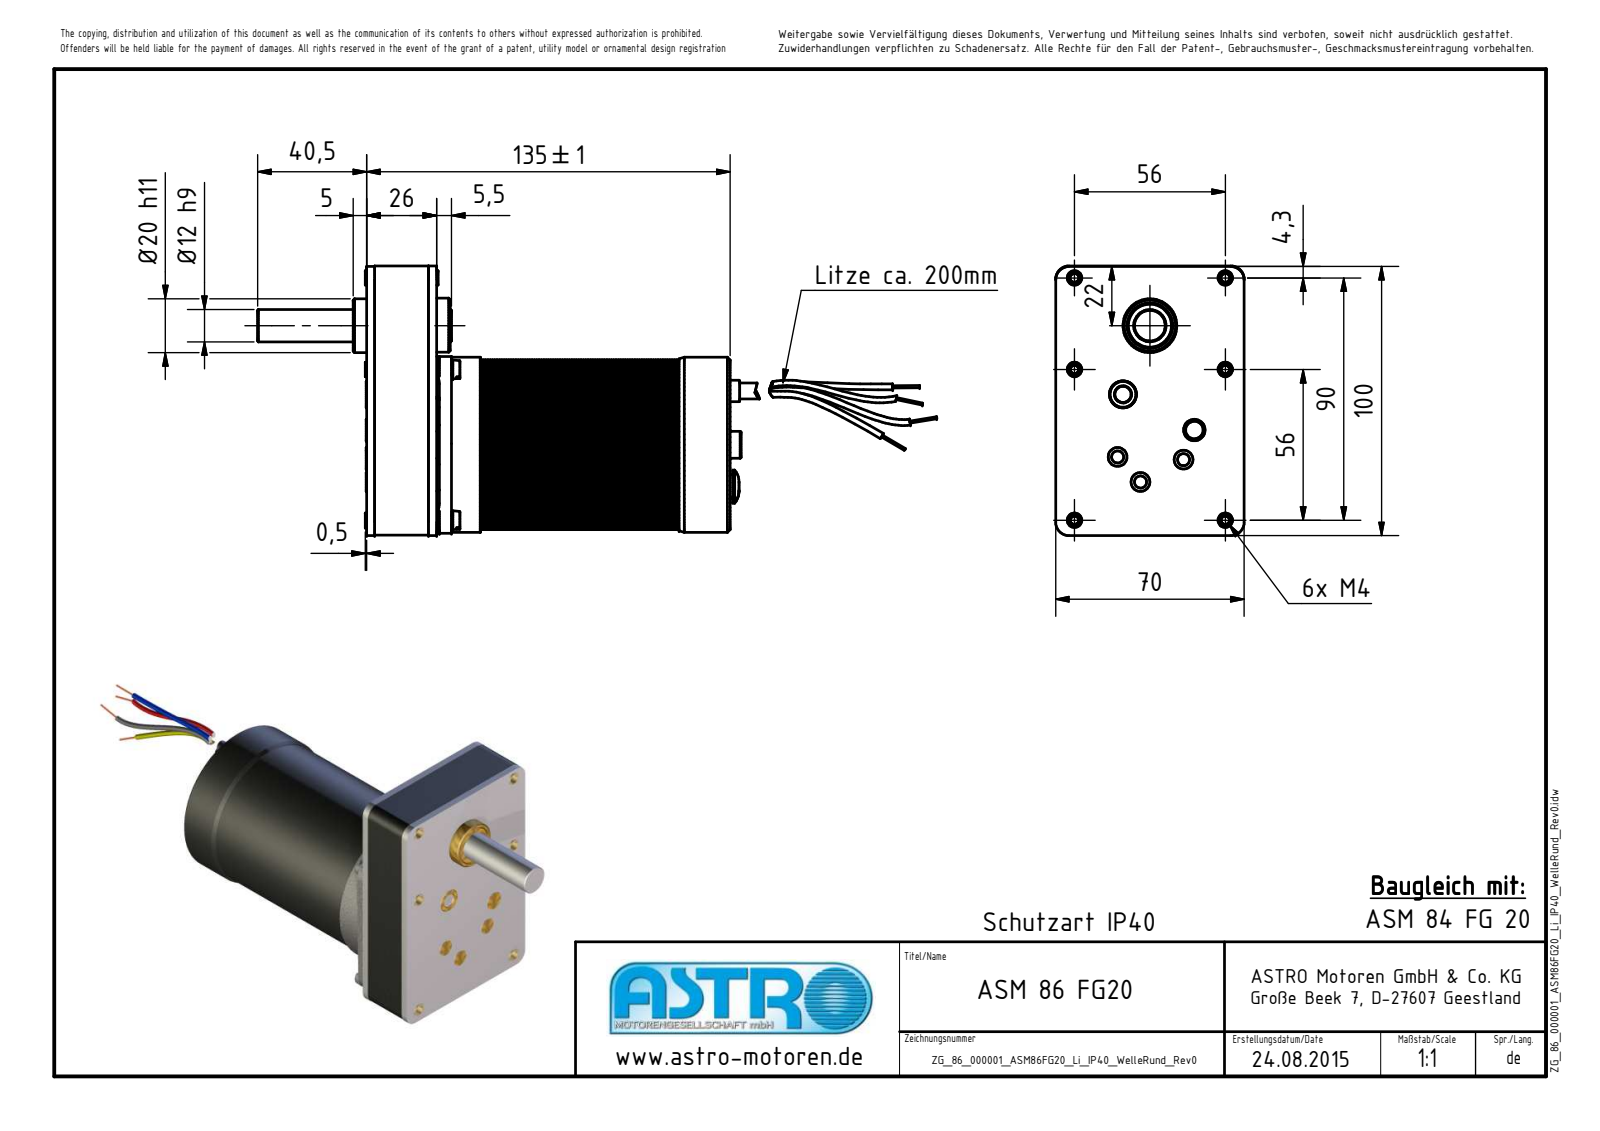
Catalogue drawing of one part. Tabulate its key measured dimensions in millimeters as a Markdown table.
| quantity | value |
| --- | --- |
| part name | ZG_86_000001_ASM86FG20_Li_IP40_WelleRund_Rev0; AFG-20rund; FG-Antriebsseite20; FG-Abstandhalter (+8 more) |
| STEP written by | Autodesk Inventor 2010 (AUTOMOTIVE_DESIGN) |
| units | millimeters |
| bodies | 148 solids, 17698 faces (6422 planar, 11163 cylindrical, 113 other) |
| overall size | 256.03 × 100.2 × 70 |
| volume | 208 032 mm³ |
| surface area | 434 105 mm² |
| round holes (diameter × count) | 1.6 × 8, 4.1 × 8, 5 × 7, 4.4 × 4, 4.5 × 3, 10 × 3, 16 × 3, 6 × 2, 5.5 × 1, 6.5 × 1, 12 × 1, 14 × 1 |
| round bosses / shafts (diameter × count) | 8 × 8, 5.39 × 6, 4.84 × 6, 15 × 4, 7 × 3, 0.8 × 3, 20 × 2, 12.01 × 2 |
| partial cylindrical surfaces (radius × count) | 0.5 × 32, 2.25 × 8, 3.5 × 8, 5 × 8, 3.15 × 4, 5.26 × 4, 11 × 1, 28.5 × 1 |
| main face-to-face distances | 0.65, 1.3, 3, 1.95, 2.6, 3.25, 3.9, 23, 4.55, 5.2 |
| hole center spacings | 47, 31.46, 11.29, 22.58, 55.42, 29.5, 41.72, 54.51 |
